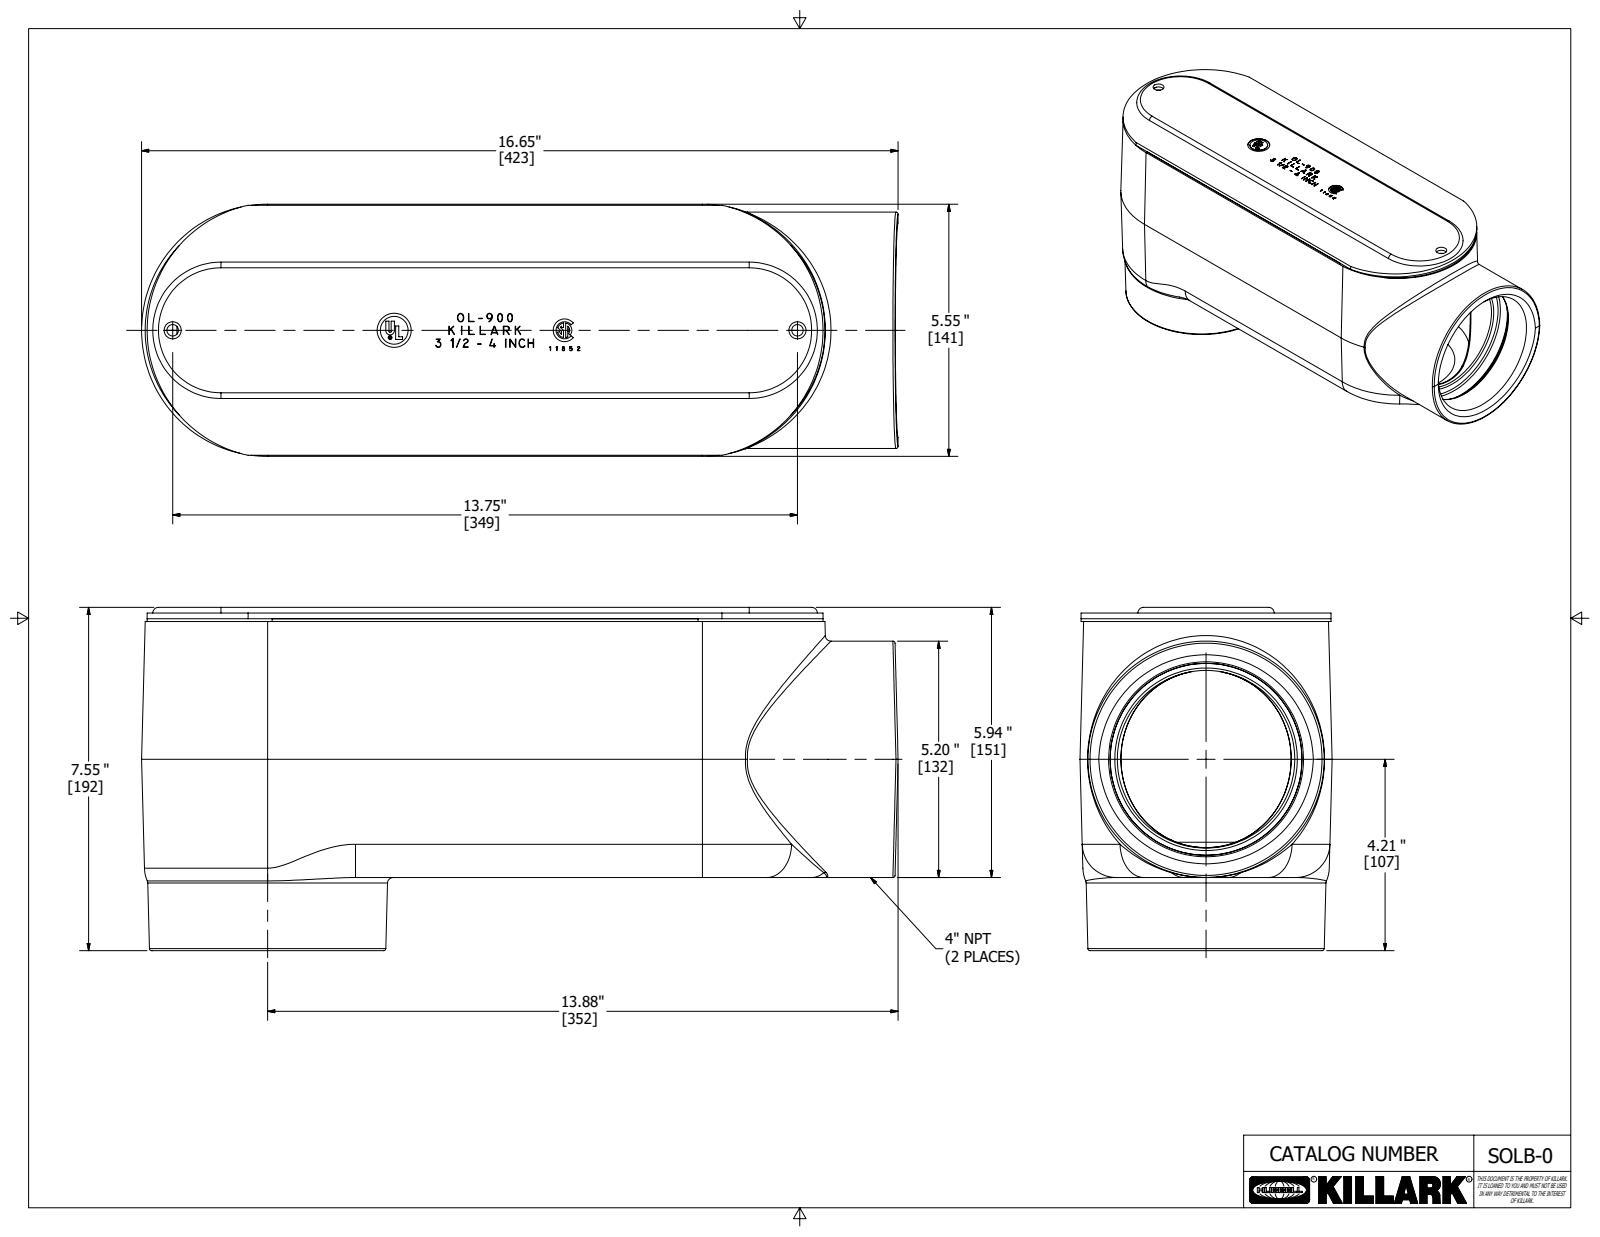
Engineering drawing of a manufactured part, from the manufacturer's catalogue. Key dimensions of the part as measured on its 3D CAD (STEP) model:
Part name (STEP PRODUCT): SOLB-0; OLB-0M; 03643; 0243900B
STEP written by: Autodesk Inventor 2020 (AUTOMOTIVE_DESIGN)
Units: inches
Bodies: 3 solids, 722 faces (262 planar, 43 cylindrical, 417 other)
Overall size (bounding box): 16.649 × 7.553 × 5.549
Volume: 100.3 in³ · Surface area: 909.1 in²
Round holes (diameter × count): ⌀0.375 ×3, ⌀0.252 ×2, ⌀4.511 ×2, ⌀0.083 ×1, ⌀0.75 ×1
Round bosses / shafts (diameter × count): ⌀5.2 ×1, ⌀0.611 ×1, ⌀0.07 ×1
Partial cylindrical surfaces — rounded edges, fillets, slot ends (radius × count): R0.09 ×4, R0.125 ×4, R0.5 ×2, R0.75 ×2, R2.75 ×2, R2.813 ×2, R0.008 ×1, R0.013 ×1
Main face-to-face distances: 0.063, 0.187, 0.125, 5.265, 0.313, 0.25, 0.125, 5.343, 5.405, 5.53
Hole centre spacings: 0.183, 2.09, 2.7, 2.785, 4.787, 4.875, 8.875, 8.875
